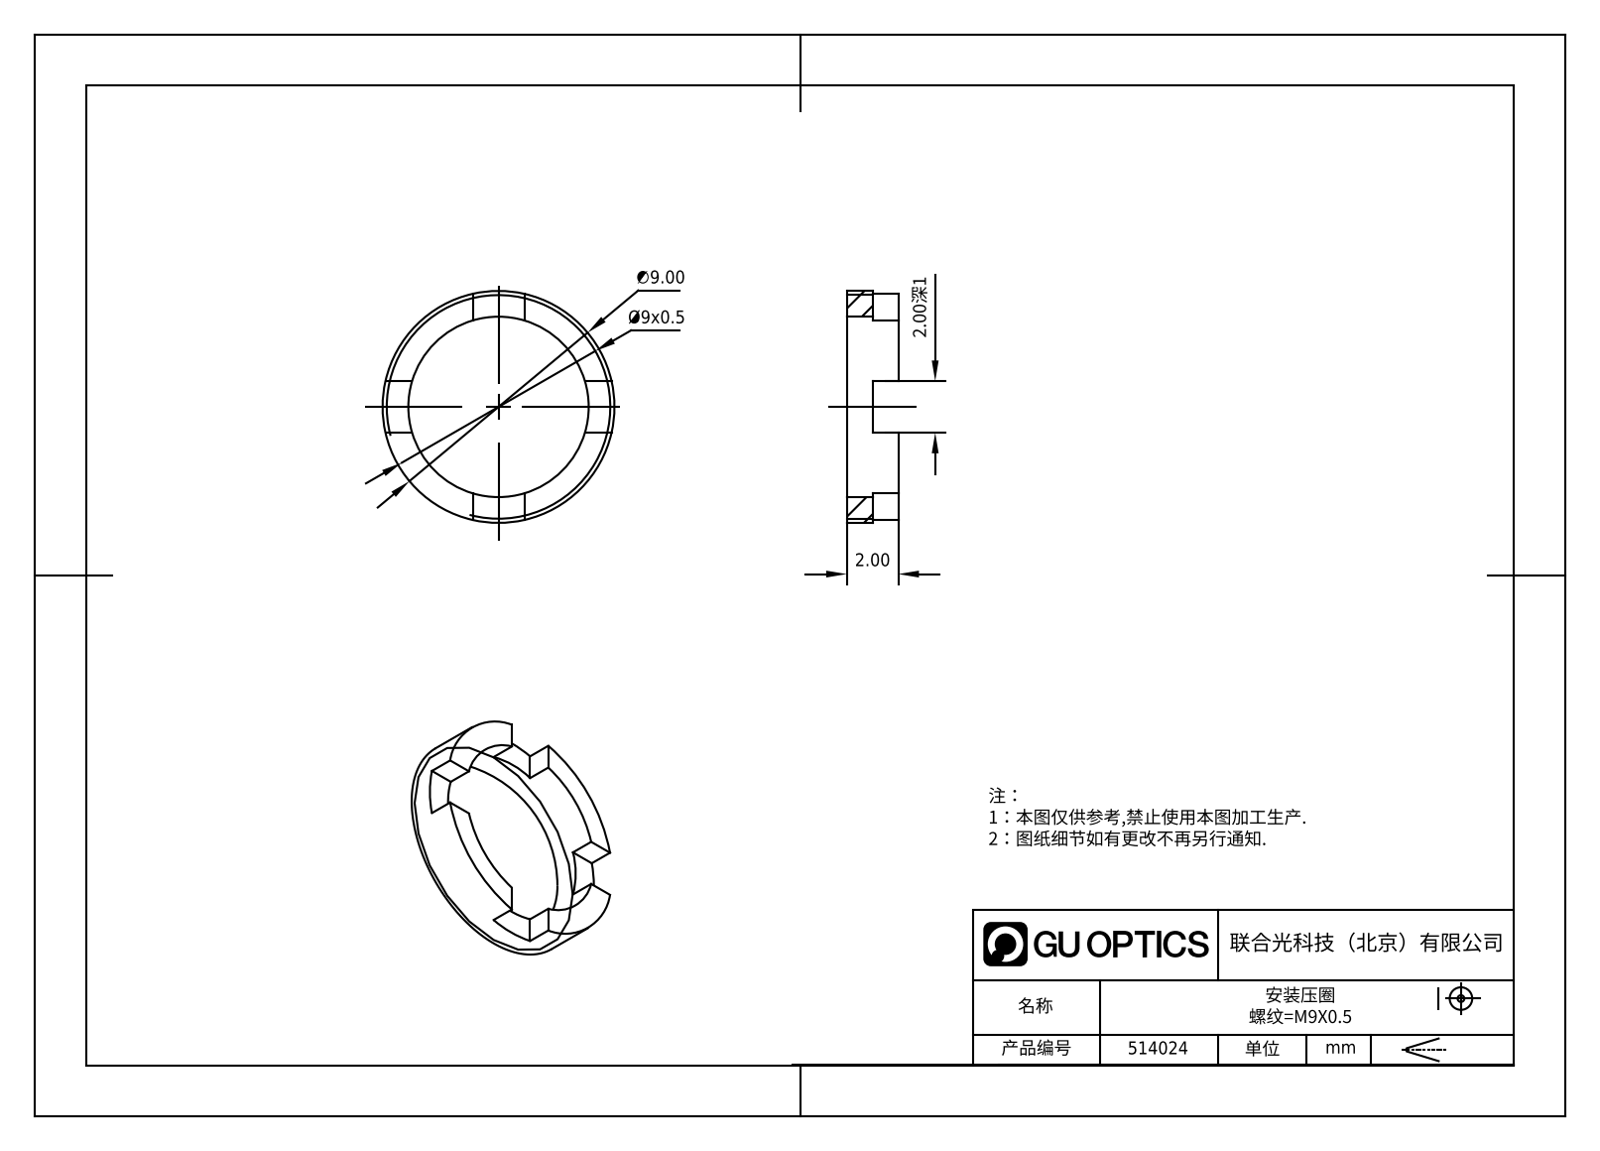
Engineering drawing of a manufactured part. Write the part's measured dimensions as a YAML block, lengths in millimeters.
part_name: "514024"
step_written_by: "SolidWorks 2020 (CONFIG_CONTROL_DESIGN)"
units: millimeters
bodies: {solids: 1, faces: 21, planar: 17, cylindrical: 4, other: 0}
overall_size: [9, 9, 2]
volume: 42
surface_area: 143
round_holes:
  - {diameter: 7, count: 1}
round_bosses_or_shafts:
  - {diameter: 9, count: 1}
face_to_face_distances: [2, 1]
